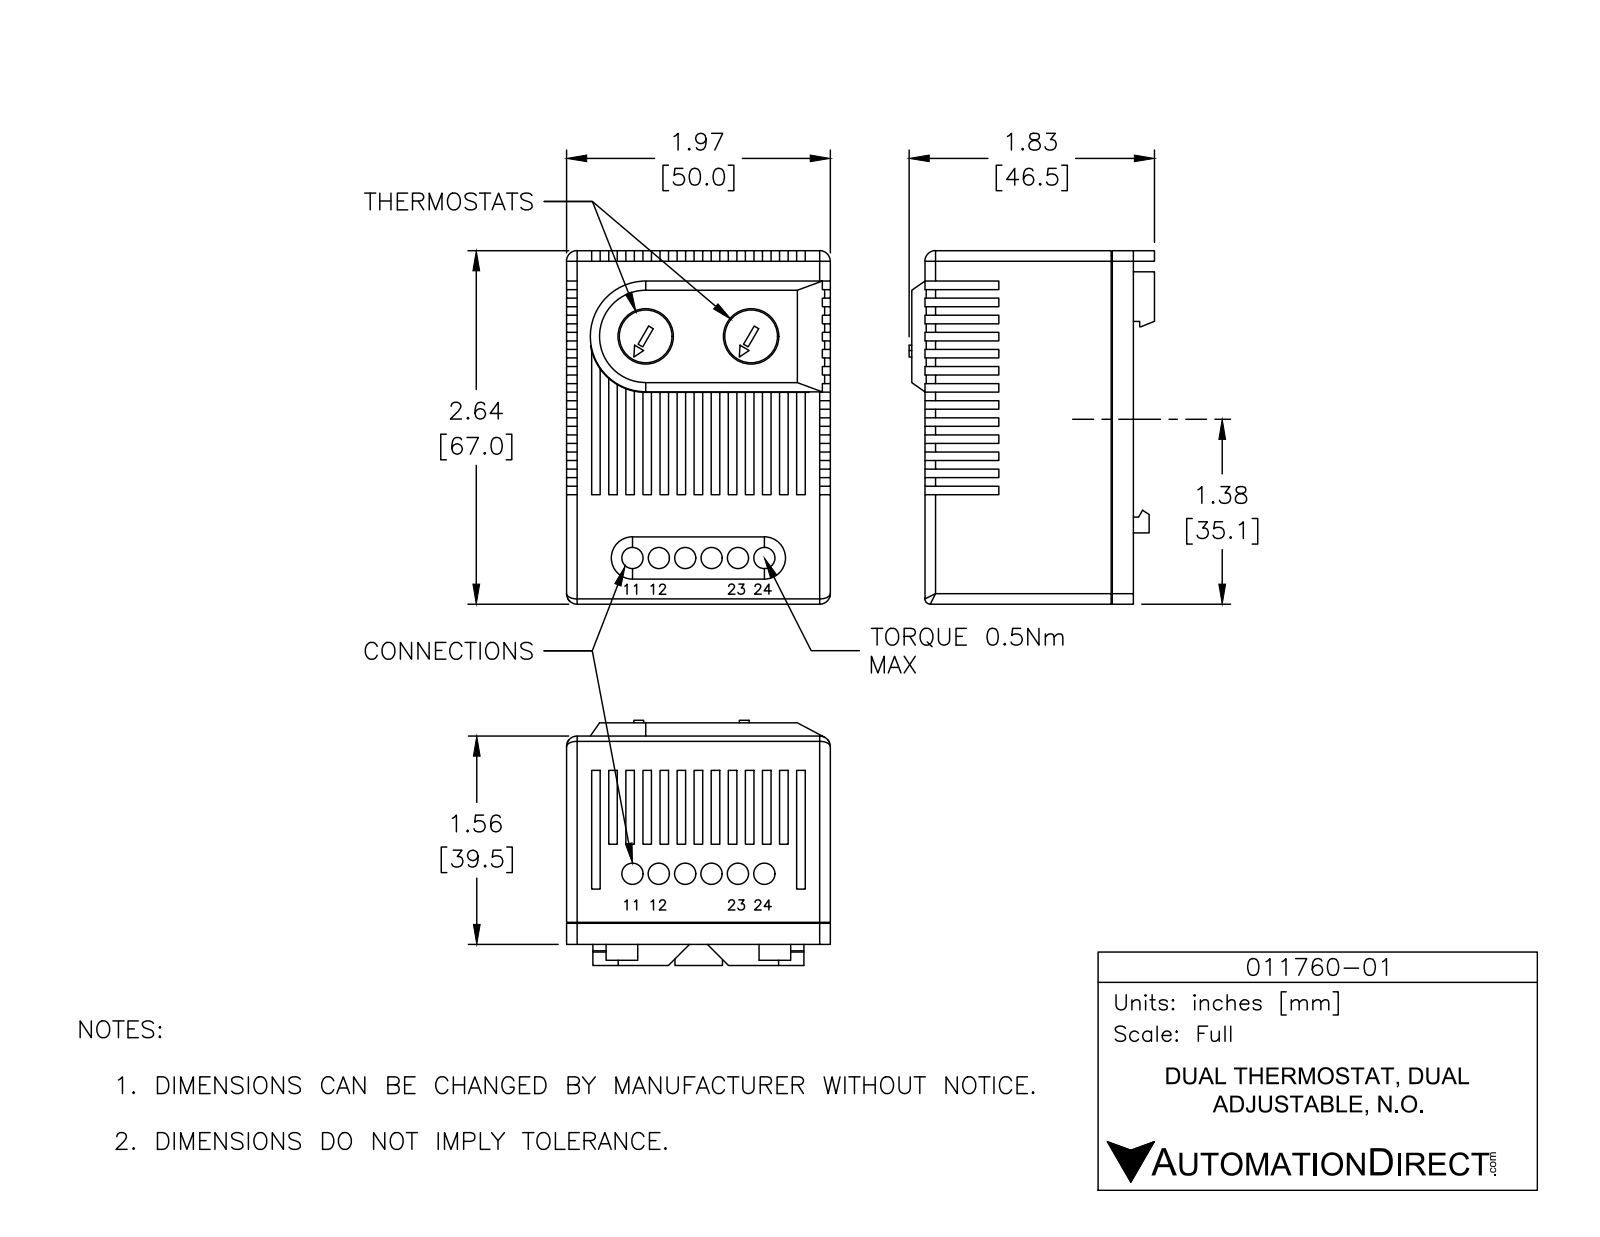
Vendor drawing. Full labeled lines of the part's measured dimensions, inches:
Part name (STEP PRODUCT): 011760-01
STEP written by: SolidWorks 2017 (AUTOMOTIVE_DESIGN)
Units: inches
Bodies: 2 solids, 656 faces (507 planar, 93 cylindrical, 56 other)
Overall size (bounding box): 2.656 × 1.969 × 1.831
Volume: 7.939 in³ · Surface area: 35.94 in²
Round holes (diameter × count): ⌀0.157 ×12, ⌀0.413 ×2
Round bosses / shafts (diameter × count): ⌀0.394 ×2
Partial cylindrical surfaces — rounded edges, fillets, slot ends (radius × count): R0.079 ×7, R0.039 ×5, R0.054 ×1, R0.06 ×1, R0.157 ×1, R0.413 ×1, R0.417 ×1
Main face-to-face distances: 1.969, 0.079, 0.128, 1.555, 2.638, 0.064, 0.255, 0.383, 0.191, 0.319
Hole centre spacings: 0.197, 0.394, 0.591, 0.787, 1.656, 0.984, 1.68, 1.725
